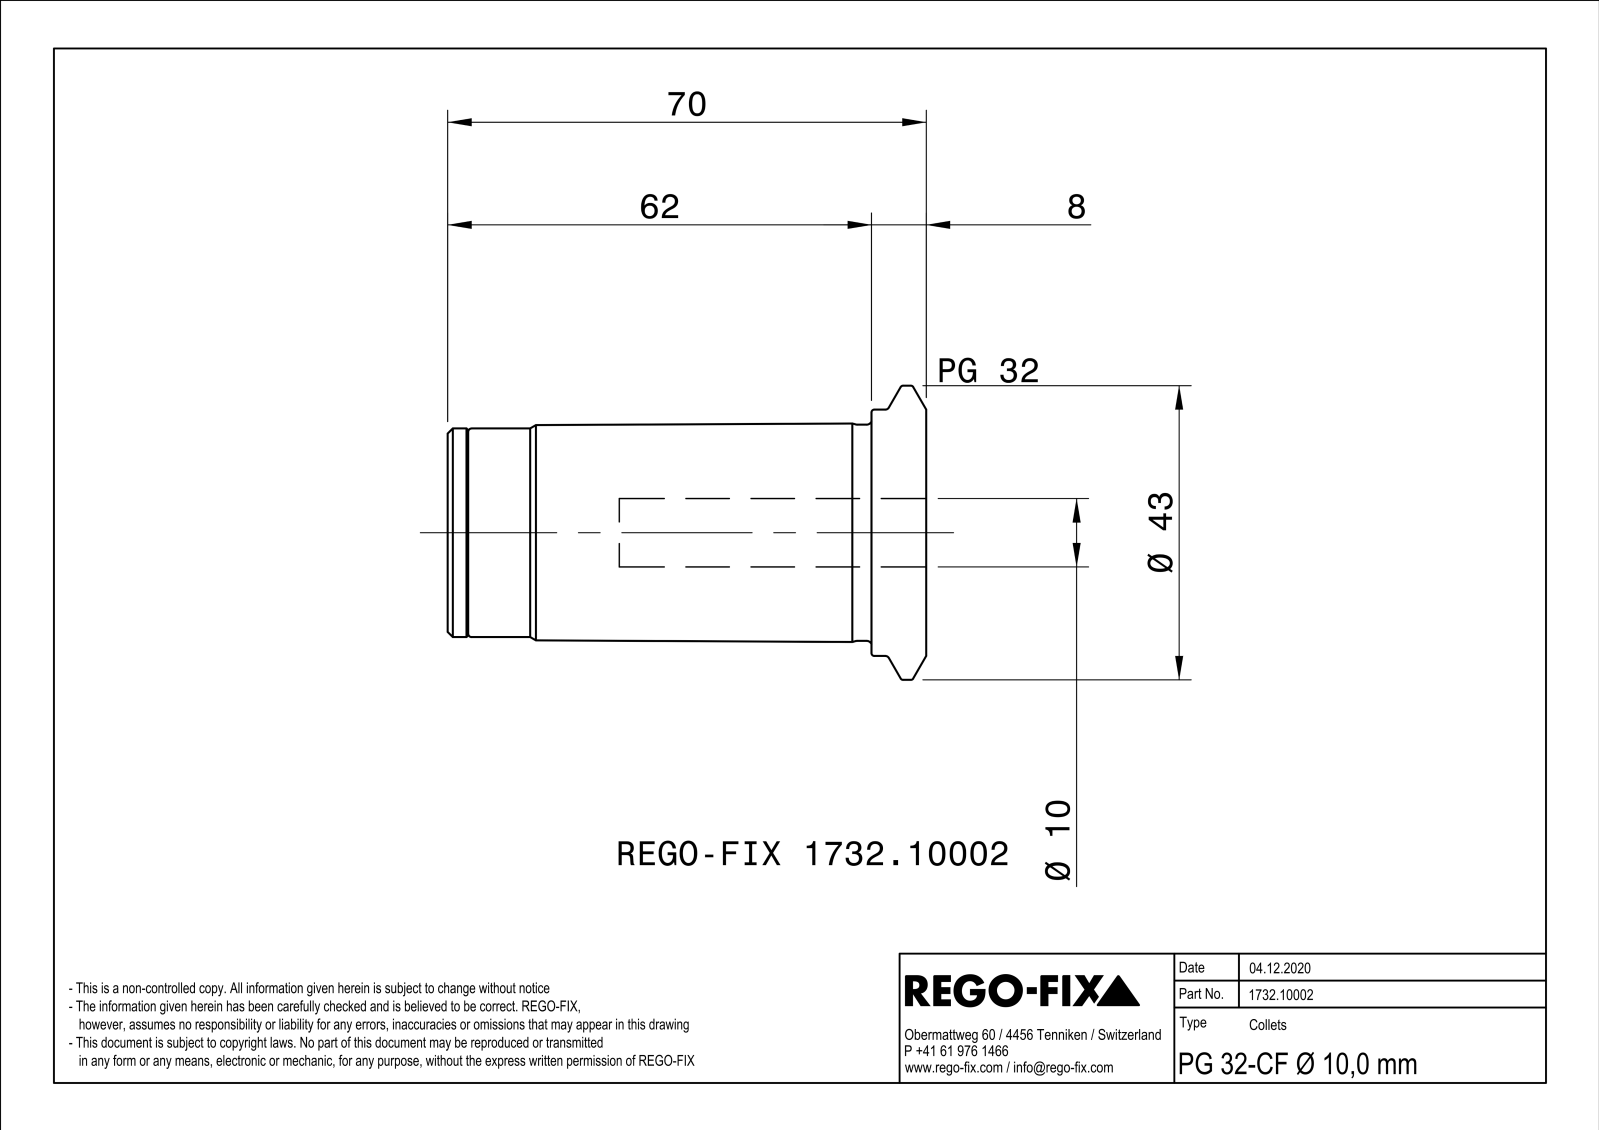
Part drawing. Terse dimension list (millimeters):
name: NOCUT
written by: SIEMENS PLM Software Solid Edge ST10 (AUTOMOTIVE_DESIGN)
unit: mm
bodies: 1 solid, 135 faces (34 planar, 46 cylindrical, 55 other)
size: 70 × 43 × 42.99
volume: 46 589 mm³; area: 16 841 mm²
holes: 3× ⌀4, 1× ⌀8.92, 1× ⌀10, 1× ⌀10.5, 1× ⌀15.5, 1× ⌀26.92, 1× ⌀28.5
bosses: 1× ⌀43, 1× ⌀36, 1× ⌀31.6, 1× ⌀30.5, 1× ⌀26.5, 1× ⌀21
rounds: 6× R2, 3× R1, 3× R3.5, 1× R3.98, 1× R4.75, 1× R8.75
face distances: 1, 70, 58, 12, 59, 11, 8, 60, 2, 10
hole spacings: 7.75, 13.42, 13.43
